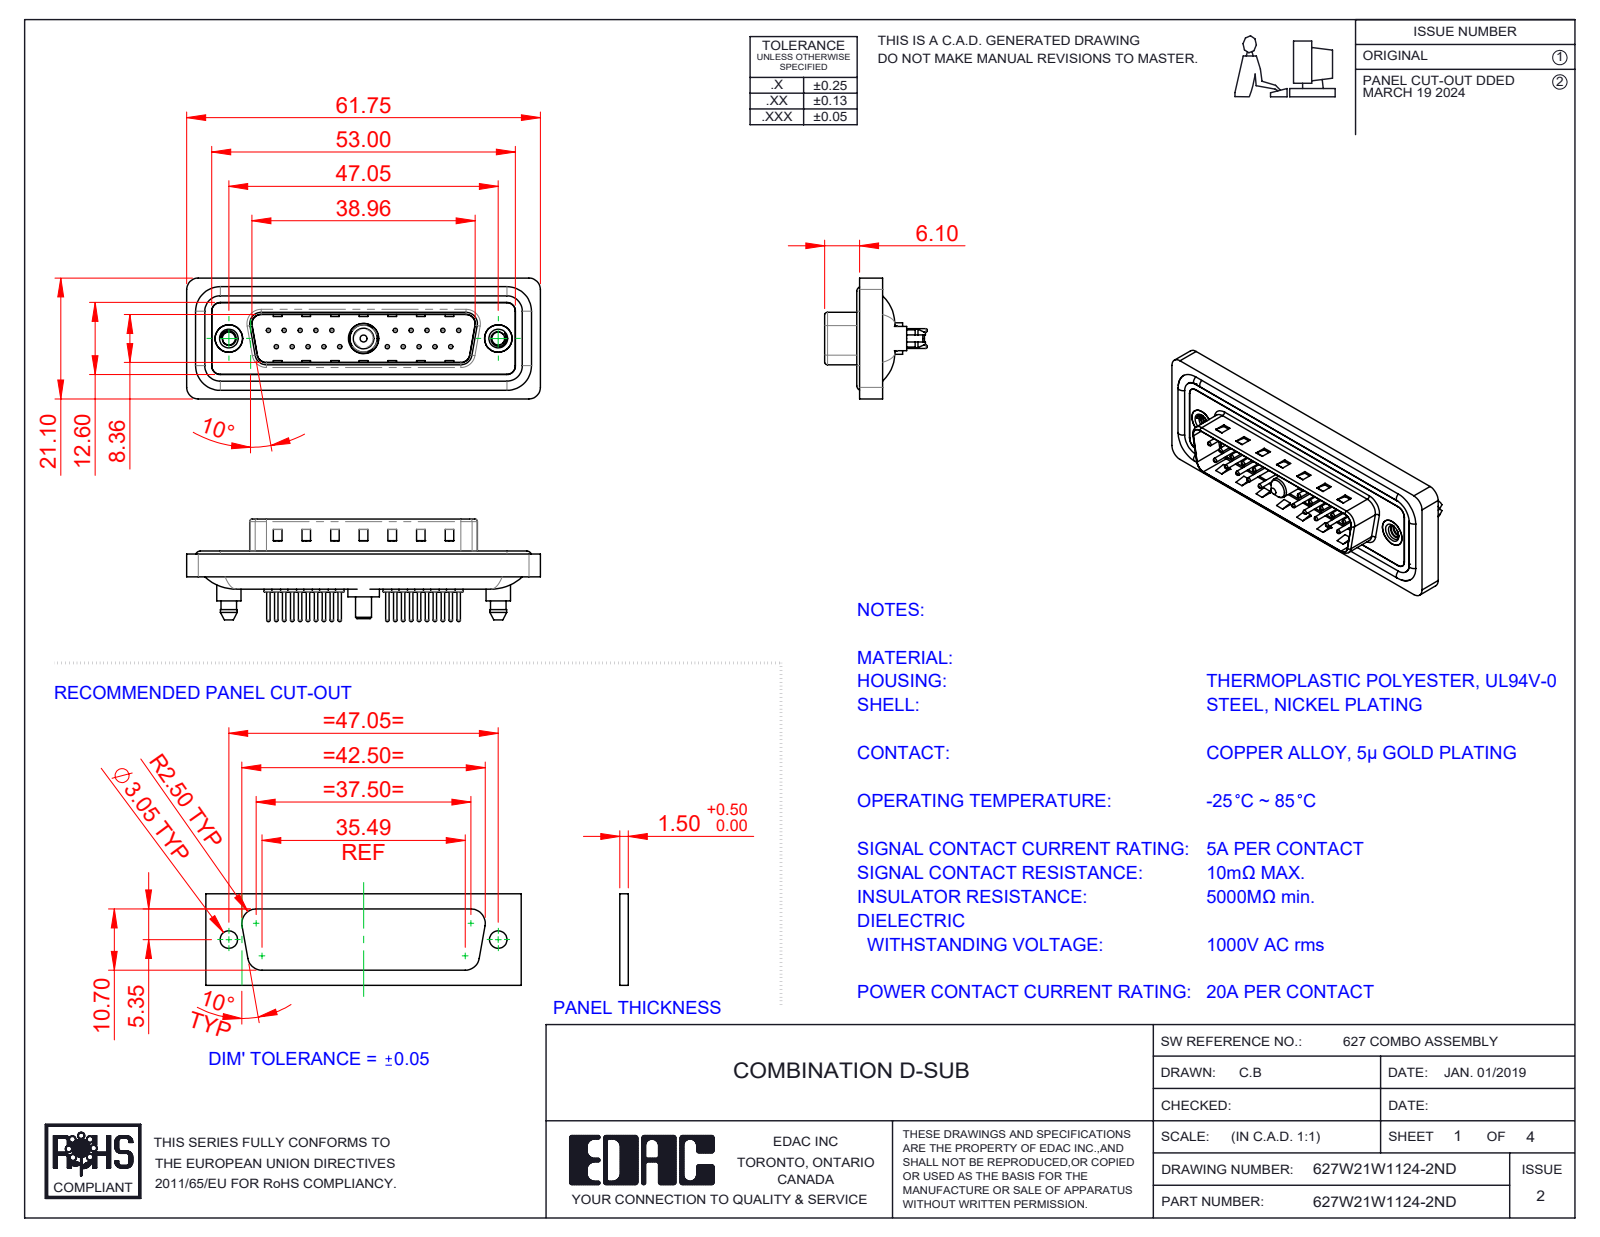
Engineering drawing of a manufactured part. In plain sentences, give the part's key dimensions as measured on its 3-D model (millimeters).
The part is named "627Combo Contact Row 2_24; 627Combo Shell Front_25 Contacts; 627Combo Waterproof Housing_25 Contacts; 627Combo Shell Rear_25 Contacts (+6 more)". Its 3-D file was written by "SolidWorks 2023 (CONFIG_CONTROL_DESIGN)". It is 29 solids with 1320 faces: 375 planar, 527 cylindrical and 418 other. Overall it measures 61.75 by 21.1 by 17.9 millimeters. Its volume is 7 332 cubic millimeters and its surface area 12 289 square millimeters. Round holes: 20 of diameter 0.75, 20 of diameter 1.6, 20 of diameter 2, 2 of diameter 2.26, 2 of diameter 4, 2 of diameter 4.8, 2 of diameter 5, 1 of diameter 4.85, 1 of diameter 5.3. Round bosses or shafts: 20 of diameter 1.5, 20 of diameter 0.6, 4 of diameter 1.6, 2 of diameter 5.4, 2 of diameter 4.9, 2 of diameter 4.25, 1 of diameter 5.5, 1 of diameter 5.2. Partial cylindrical surfaces (rounded edges, fillets, slot ends): 24 of radius 1.5, 18 of radius 2, 10 of radius 1.6, 8 of radius 0.5, 4 of radius 0.25, 4 of radius 0.6, 4 of radius 0.65, 4 of radius 0.9. The main face-to-face distances are 0.4, 1.5, 1.1, 1.6, 0.5, 3.1, 2.9, 4.1, 0.82, 9.58. The hole center spacings are 3.16, 2.77, 5.54, 8.31, 5.04, 19.39, 20.97, 22.16.
